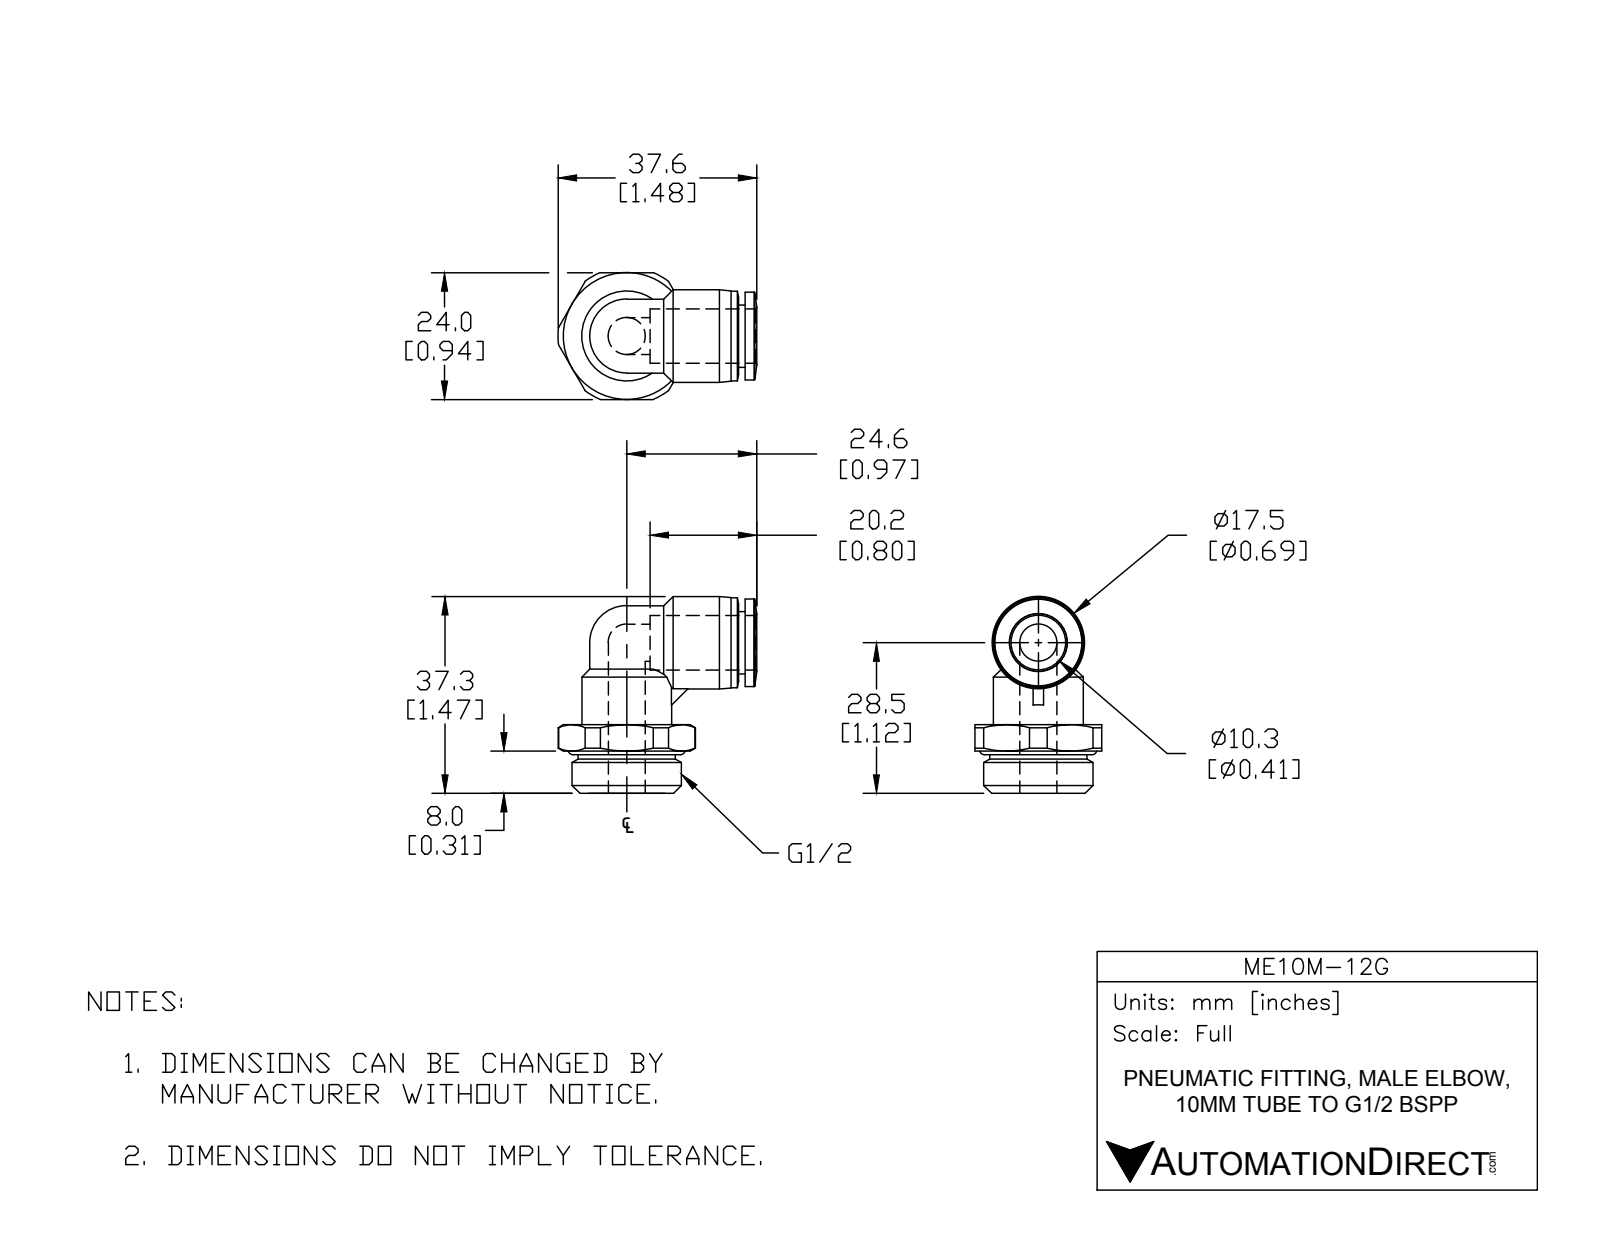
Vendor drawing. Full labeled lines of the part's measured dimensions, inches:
Part name (STEP PRODUCT): ME10M-12G
STEP written by: SolidWorks 2018 (AUTOMOTIVE_DESIGN)
Units: inches
Bodies: 2 solids, 87 faces (18 planar, 30 cylindrical, 39 other)
Overall size (bounding box): 1.48 × 1.467 × 0.945
Volume: 0.61 in³ · Surface area: 9.063 in²
Round holes (diameter × count): ⌀0.276 ×2, ⌀0.406 ×1
Round bosses / shafts (diameter × count): ⌀0.669 ×2, ⌀0.815 ×1, ⌀0.724 ×1, ⌀0.689 ×1, ⌀0.654 ×1, ⌀0.551 ×1, ⌀0.465 ×1
Partial cylindrical surfaces — rounded edges, fillets, slot ends (radius × count): R0.276 ×1, R0.512 ×1
Main face-to-face distances: 0.512, 0.945, 0.049, 0.659, 0.709, 0.315, 0.197, 0.362, 0.047, 0.15
